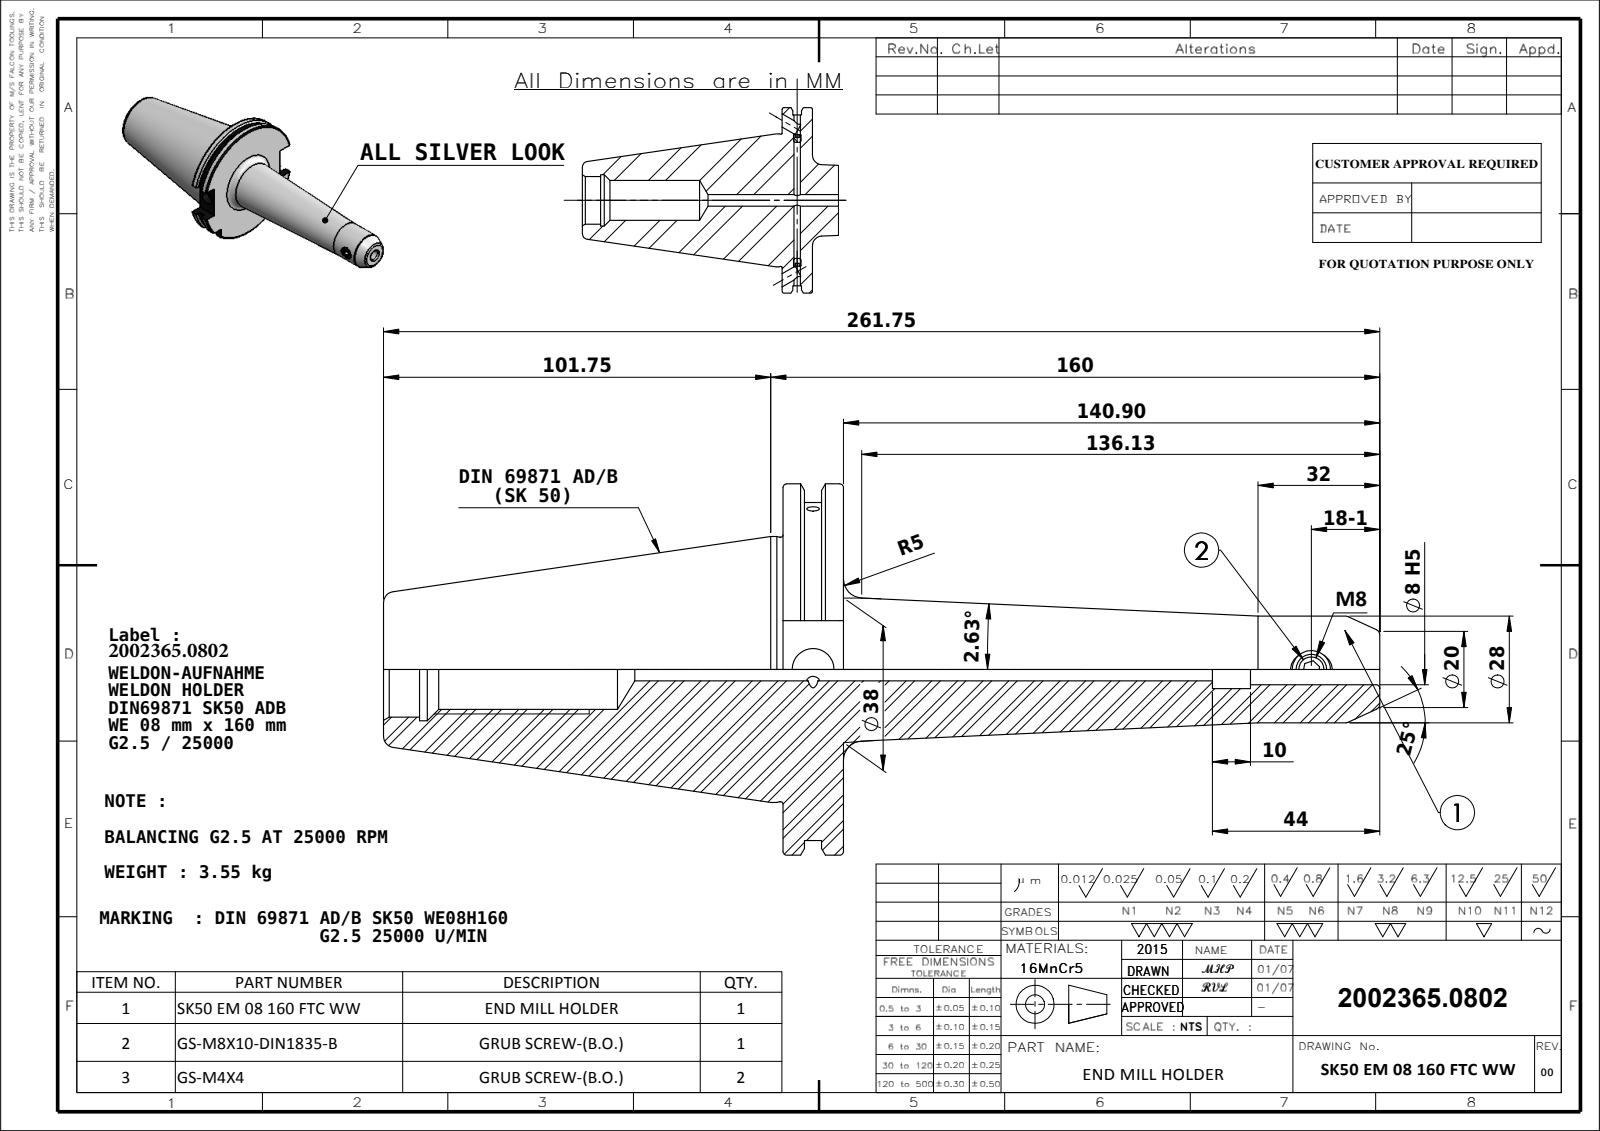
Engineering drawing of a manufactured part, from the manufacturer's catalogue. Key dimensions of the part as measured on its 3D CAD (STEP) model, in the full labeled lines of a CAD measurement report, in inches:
Part name (STEP PRODUCT): SK50 EM 08 160 FTC WW; 91506-WE708160; M8X10._DIN 913 - M8 x 8-N; M4X4_DIN 913 - M4 x 4-N
STEP written by: SolidWorks 2009 (CONFIG_CONTROL_DESIGN)
Units: inches
Bodies: 4 solids, 170 faces (53 planar, 55 cylindrical, 62 other)
Overall size (bounding box): 10.305 × 3.839 × 3.703
Volume: 27.06 in³ · Surface area: 92.31 in²
Round holes (diameter × count): ⌀0.236 ×3, ⌀0.394 ×2, ⌀0.13 ×1, ⌀0.268 ×1, ⌀0.315 ×1, ⌀0.433 ×1, ⌀0.827 ×1, ⌀0.984 ×1, ⌀1.063 ×1
Round bosses / shafts (diameter × count): ⌀0.157 ×2, ⌀2.75 ×1, ⌀2.734 ×1, ⌀1.102 ×1, ⌀0.315 ×1
Partial cylindrical surfaces — rounded edges, fillets, slot ends (radius × count): R1.768 ×1, R1.919 ×1
Main face-to-face distances: 0.626, 0.223, 0.403, 0.4, 0.177, 0.226, 4.132, 4.355, 4.531, 4.758
Hole centre spacings: 5.154
